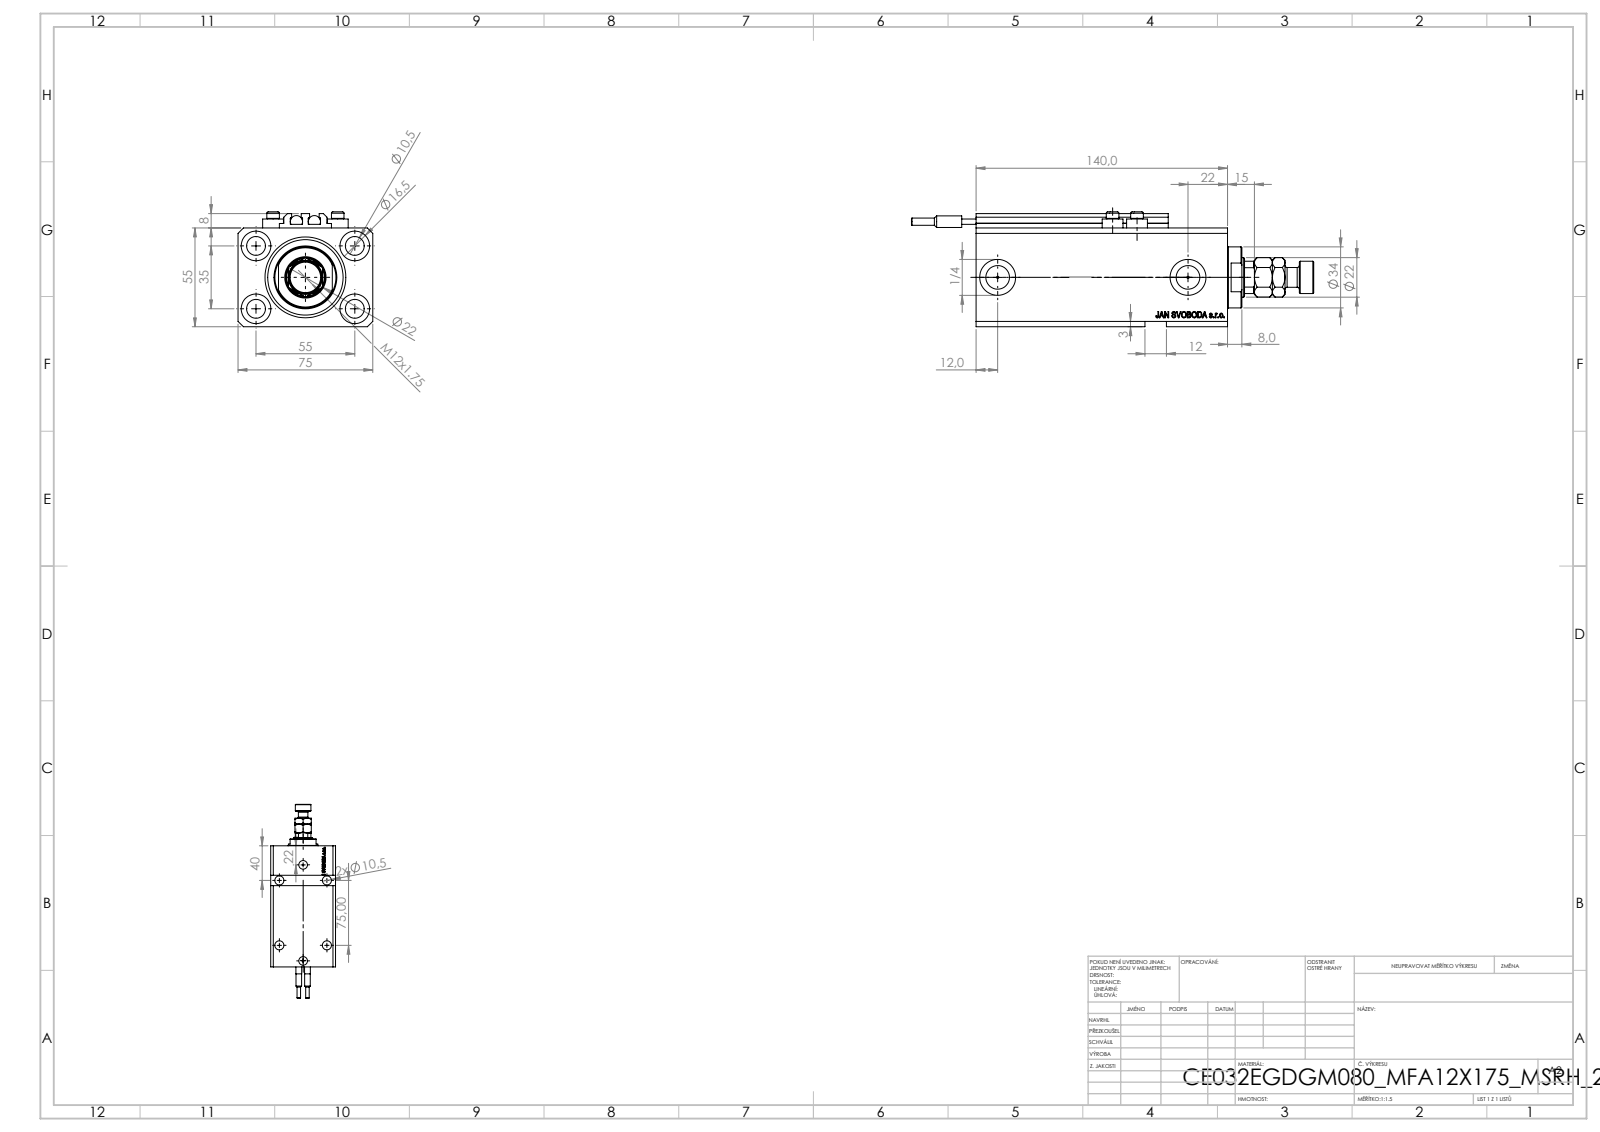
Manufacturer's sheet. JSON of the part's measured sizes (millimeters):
{"part_name": "MFA; V250CE_VC_E; V250CE_E_Body; V250CE_C_VCP (+2 more)", "step_written_by": "SolidWorks 2019 (CONFIG_CONTROL_DESIGN)", "units": "millimeters", "bodies": {"solids": 11, "faces": 1204, "planar": 566, "cylindrical": 174, "other": 464}, "overall_size": [224, 75, 64], "volume_mm3": 493240, "surface_area_mm2": 121899, "round_holes": [[10.5, 9], [1.25, 4], [4, 4], [16.5, 4], [10, 2], [13.16, 2], [20, 2], [22, 1], [32, 1], [45, 1]], "round_bosses_or_shafts": [[11.6, 4], [7, 4], [6.8, 2], [6.5, 2], [4, 2], [34, 1], [18, 1], [11, 1]], "partial_cylinders_radius": [[0.2, 10], [10.5, 1]], "face_to_face_distances": [55, 75, 15, 57, 3, 140, 9.9, 125, 2.5, 2], "hole_center_spacings": [32.6, 32.87, 55, 96.98, 13.6, 14.09, 25.81, 32.58]}
